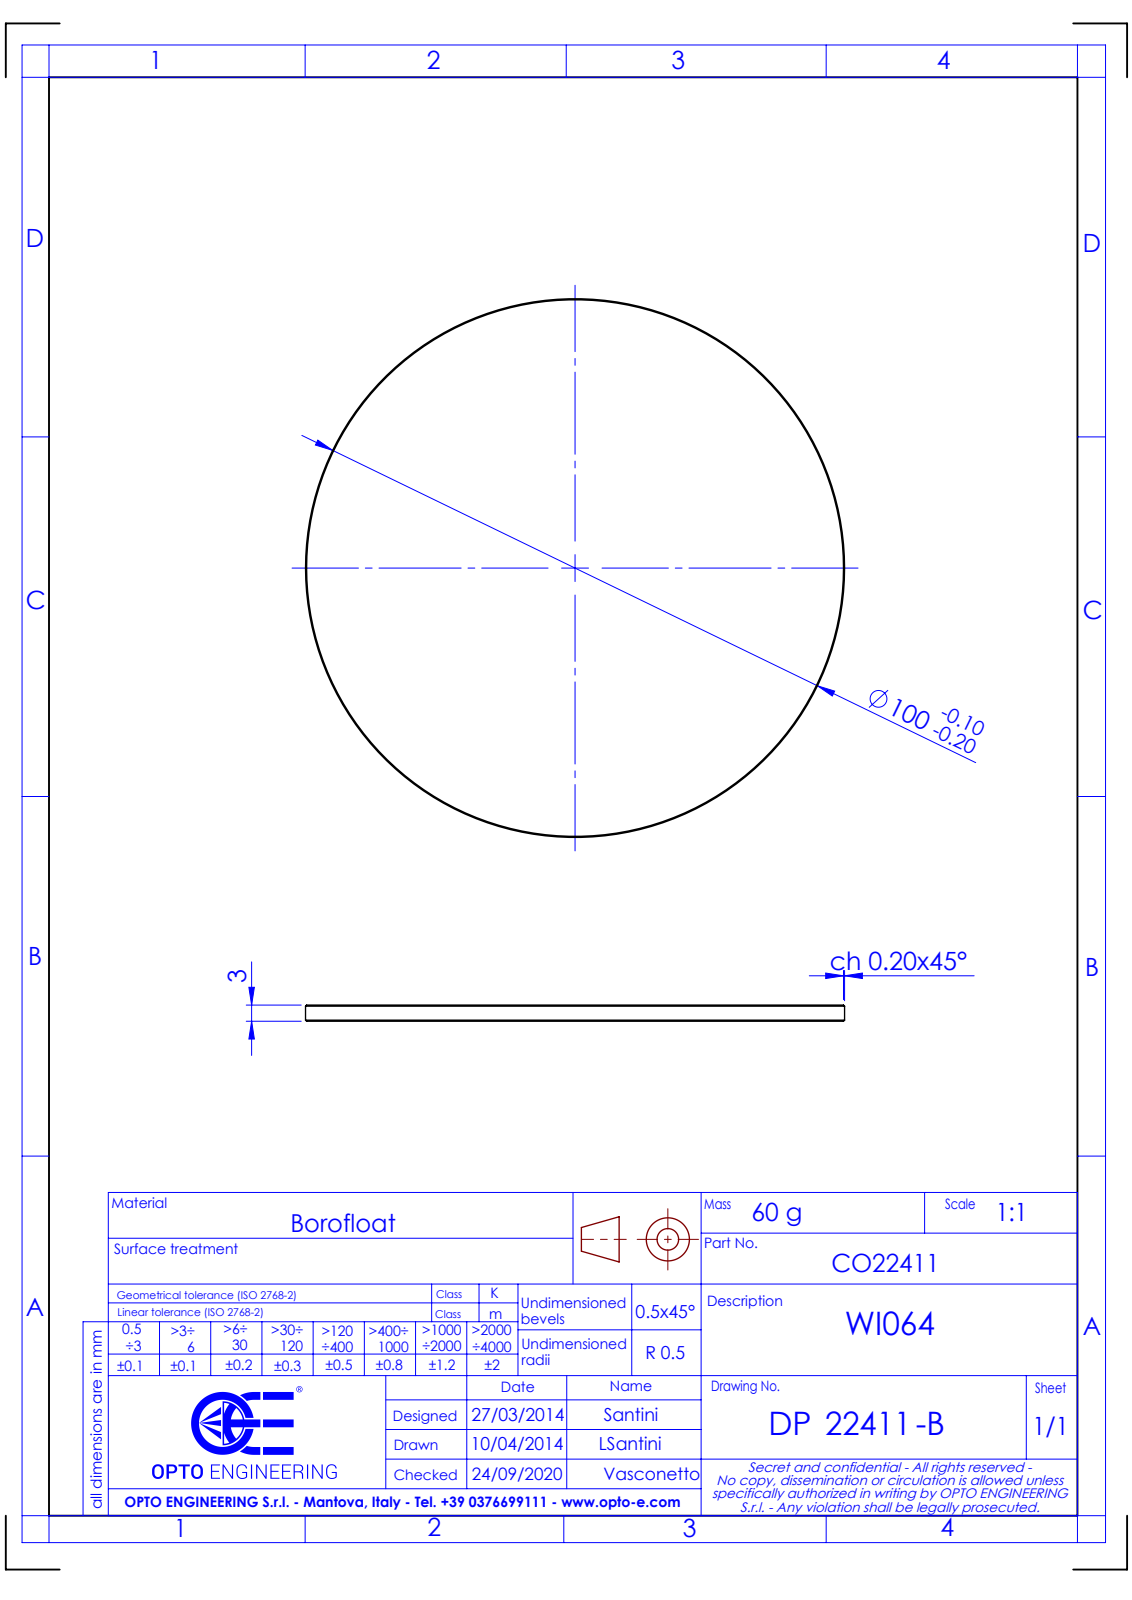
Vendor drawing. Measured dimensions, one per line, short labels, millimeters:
name: DP22411_WI064
written by: SolidWorks 2021 (CONFIG_CONTROL_DESIGN)
unit: mm
bodies: 1 solid, 8 faces (2 planar, 2 cylindrical, 4 other)
size: 100 × 100 × 3
volume: 23 549 mm³; area: 16 577 mm²
bosses: 1× ⌀100
face distances: 3
